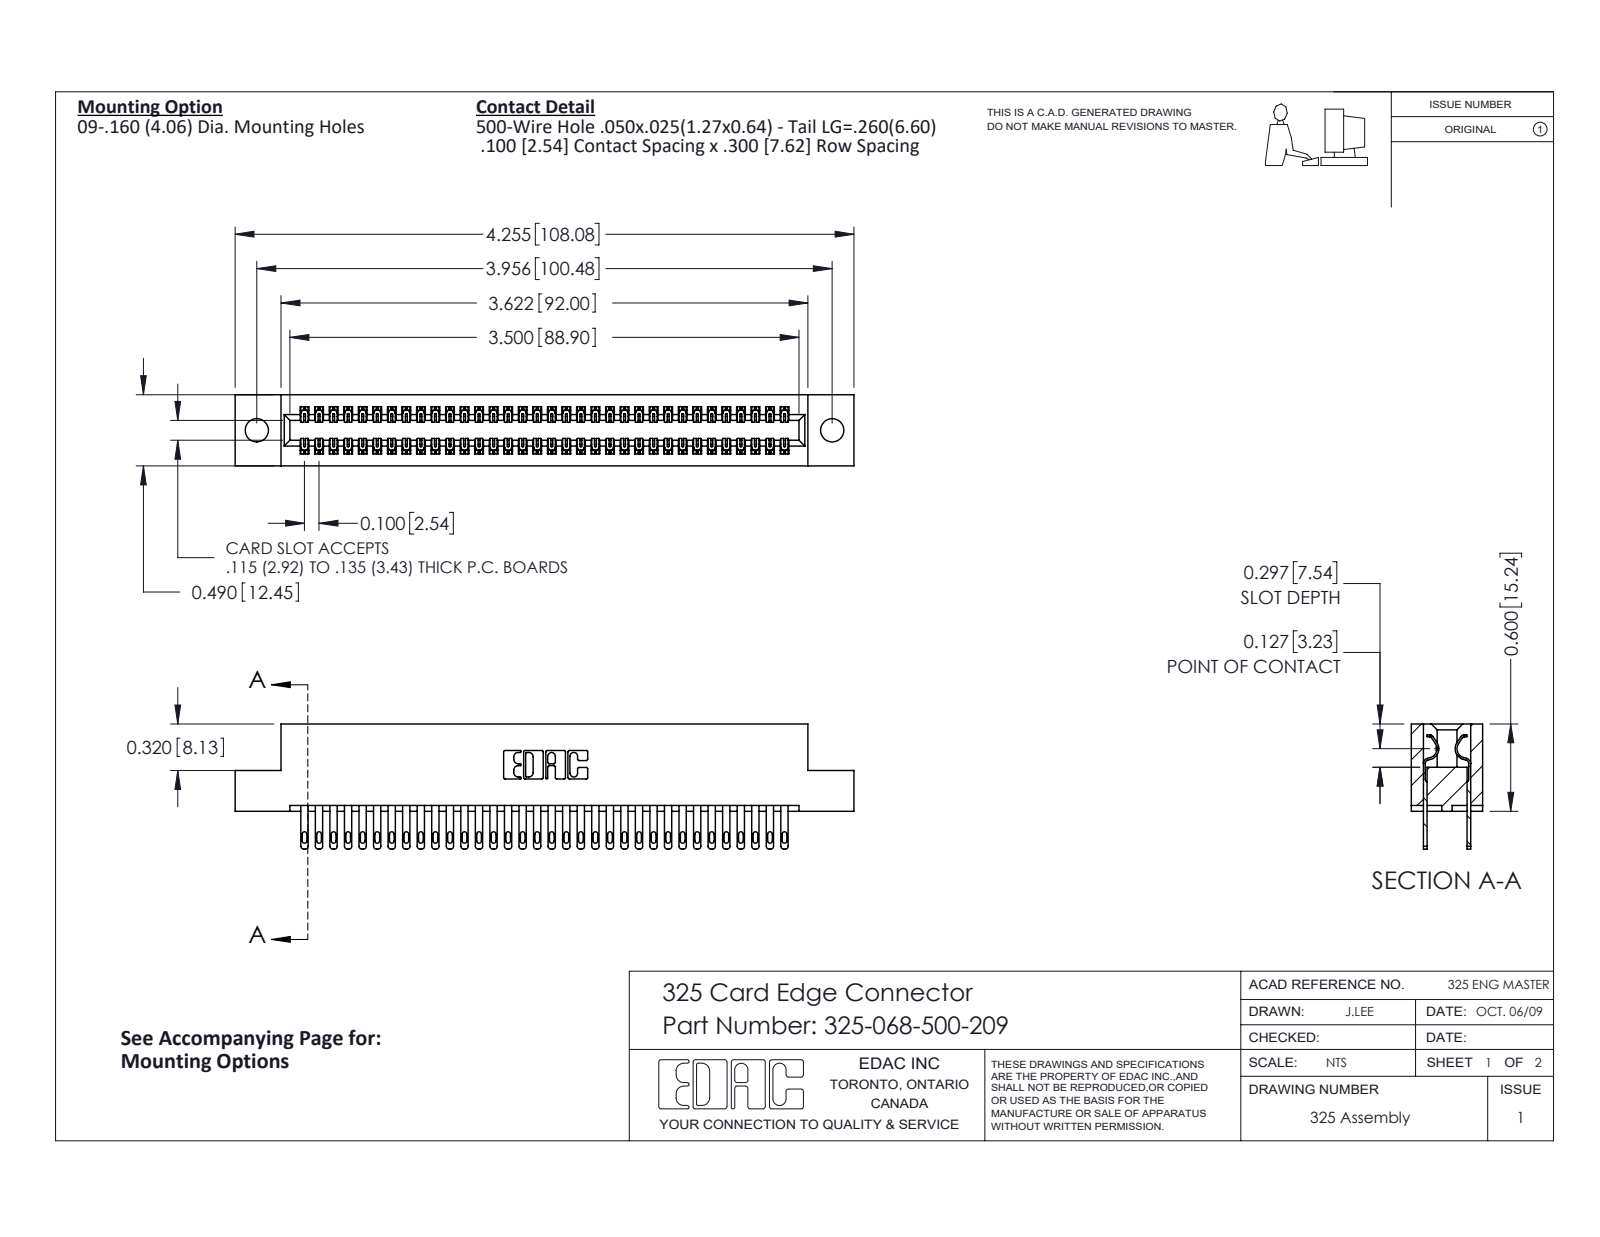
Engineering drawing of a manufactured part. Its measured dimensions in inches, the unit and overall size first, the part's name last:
Units: inches
Overall size (bounding box): 4.255 × 0.86 × 0.49
Round holes (diameter × count): ⌀0.16 ×2
Partial cylindrical surfaces — rounded edges, fillets, slot ends (radius × count): R0.006 ×102, R0.016 ×68, R0.02 ×68, R0.01 ×22, R0.007 ×6, R0.031 ×6, R0.026 ×3, R0.014 ×2
Main face-to-face distances: 0.083, 0.407, 0.3, 0.107, 0.383, 0.025, 0.49, 0.325, 0.275, 0.04
Hole centre spacings: 3.956
Volume: 0.846 in³ · Surface area: 26.68 in²
Bodies: 69 solids, 3378 faces (2110 planar, 1268 cylindrical, 0 other)
Part name (STEP PRODUCT): 325-068-500-209; 325-292-001_325-293-100; 325 Part_.160 TH
STEP written by: SolidWorks 2016 (CONFIG_CONTROL_DESIGN)
